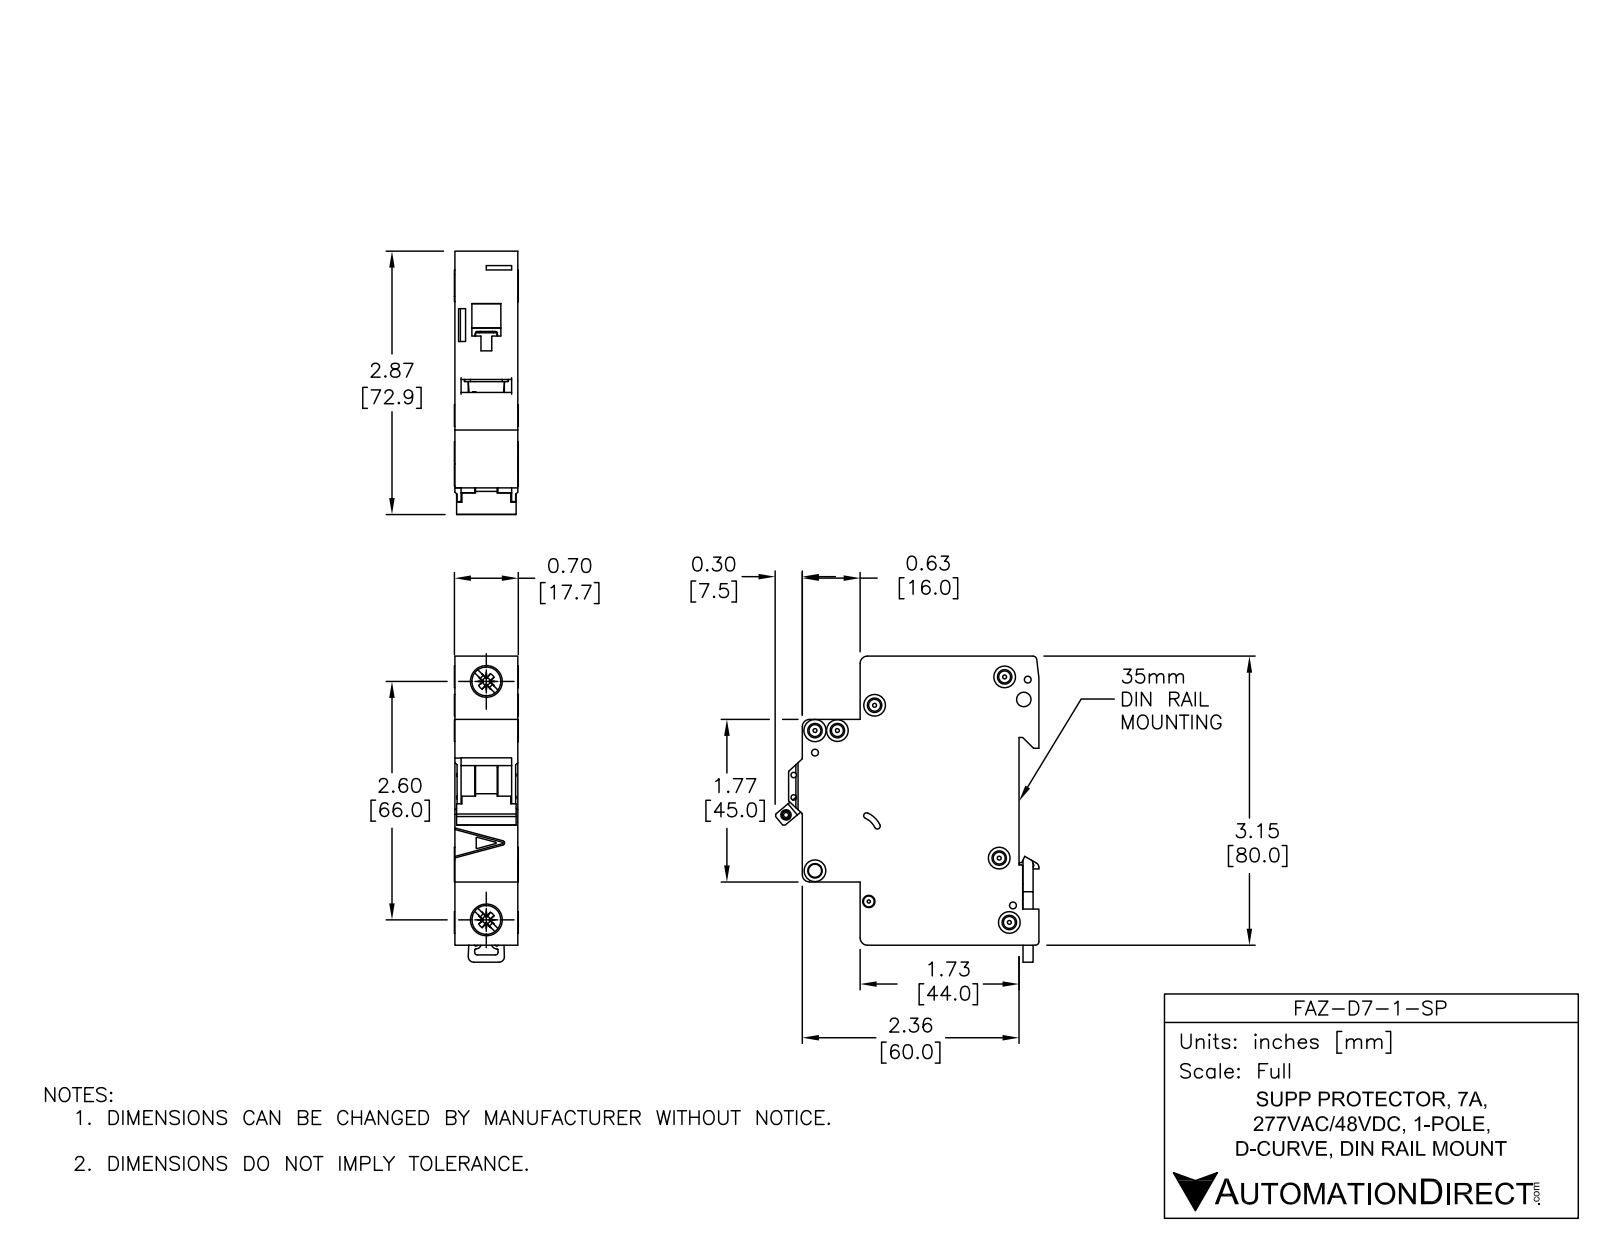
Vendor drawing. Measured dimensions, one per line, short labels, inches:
name: FAZ-D7-1-SP
written by: SolidWorks 2014 (AUTOMOTIVE_DESIGN)
unit: in
bodies: 5 solids, 558 faces (235 planar, 202 cylindrical, 121 other)
size: 3.338 × 2.876 × 0.697
volume: 4.573 in³; area: 30.29 in²
holes: 6× ⌀0.142, 3× ⌀0.075, 2× ⌀0.043, 2× ⌀0.059, 2× ⌀0.157, 2× ⌀0.281, 1× ⌀0.085, 1× ⌀0.087, 1× ⌀0.1, 1× ⌀0.13, 1× ⌀0.134
bosses: 4× ⌀0.236, 2× ⌀0.323, 1× ⌀0.098
rounds: 30× R0.01, 13× R0.02, 8× R0.079, 5× R0.008, 4× R0.039, 2× R0.031, 2× R0.118, 1× R0.059
face distances: 0.689, 3.129, 0.217, 1.949, 1.732, 2.579, 2.362, 0.63, 0.069, 0.62
hole spacings: 0.244, 0.537, 0.189, 0.204, 0.221, 0.24, 0.254, 0.322
